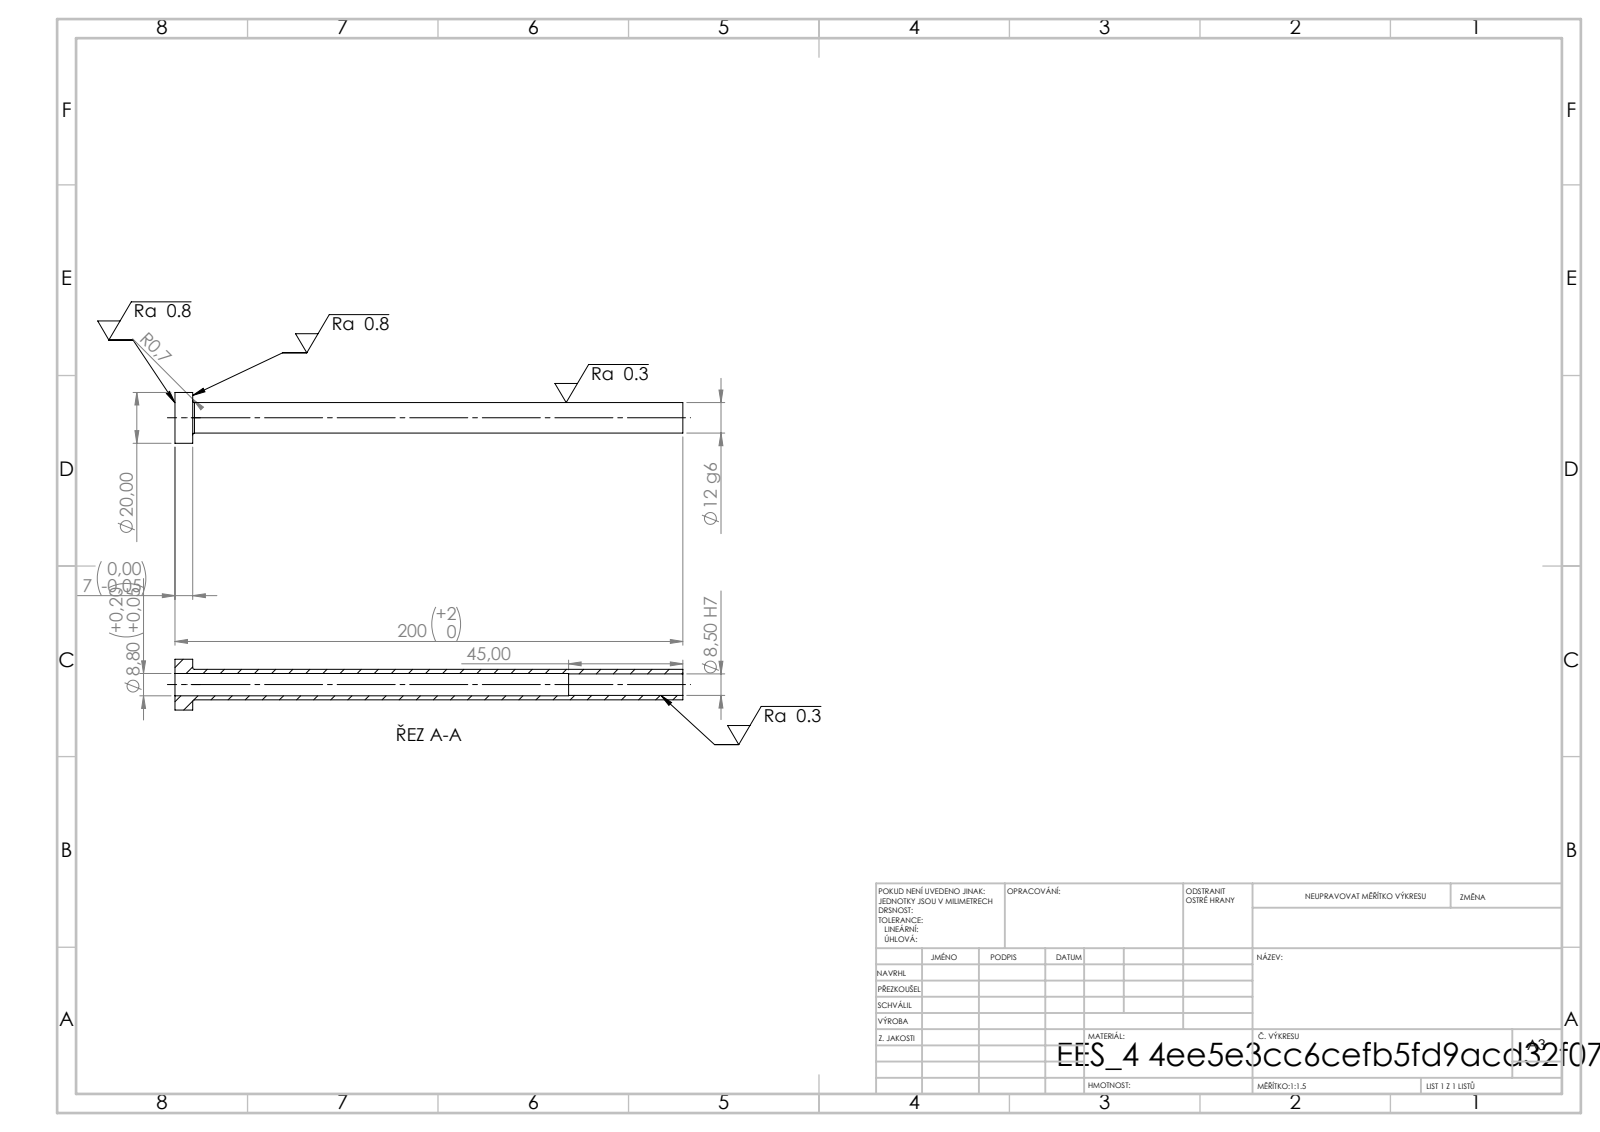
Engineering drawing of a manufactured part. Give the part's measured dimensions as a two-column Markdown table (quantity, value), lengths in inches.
| quantity | value |
| --- | --- |
| STEP written by | SolidWorks 2019 (CONFIG_CONTROL_DESIGN) |
| units | inches |
| bodies | 1 solid, 14 faces (4 planar, 8 cylindrical, 2 other) |
| overall size | 7.874 × 0.787 × 0.787 |
| volume | 0.735 in³ |
| surface area | 21.24 in² |
| round holes (diameter × count) | 0.335 × 1, 0.346 × 1 |
| round bosses / shafts (diameter × count) | 0.787 × 1, 0.472 × 1 |
| main face-to-face distances | 0.276, 7.874, 7.598, 6.102, 5.827, 1.772 |
